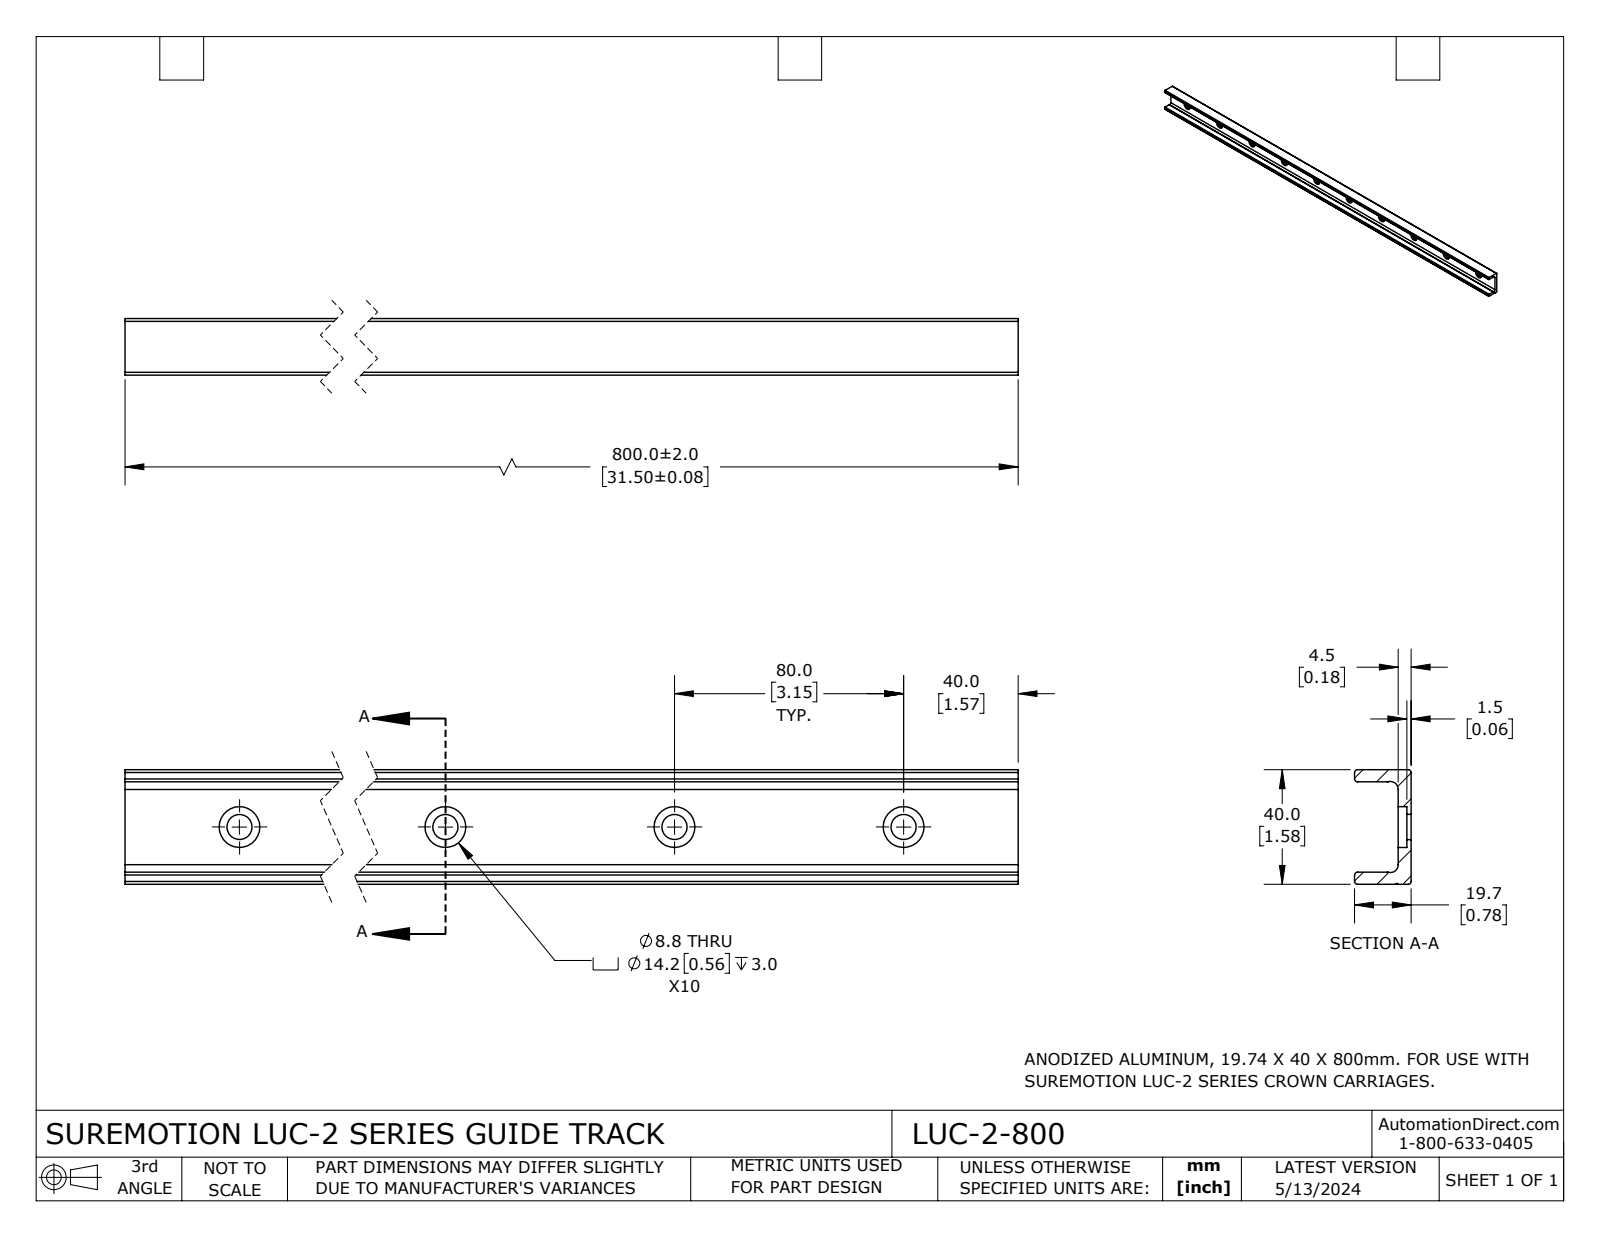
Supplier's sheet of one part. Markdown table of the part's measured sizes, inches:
| quantity | value |
| --- | --- |
| part name | LUC-2-800 |
| STEP written by | SolidWorks 2023 (CONFIG_CONTROL_DESIGN) |
| units | inches |
| bodies | 1 solid, 72 faces (21 planar, 51 cylindrical, 0 other) |
| overall size | 31.496 × 1.575 × 0.777 |
| volume | 14.81 in³ |
| surface area | 182.5 in² |
| round holes (diameter × count) | 0.347 × 10, 0.561 × 10 |
| partial cylindrical surfaces (radius × count) | 0.039 × 8, 0.109 × 2, 0.013 × 1 |
| main face-to-face distances | 0.177, 0.168, 1.408, 1.576, 1.24, 0.777, 0.6, 0.059, 0.118, 0.718 |
| hole center spacings | 3.15, 6.299, 9.449, 12.598, 15.748, 18.898, 22.047, 25.197 |
